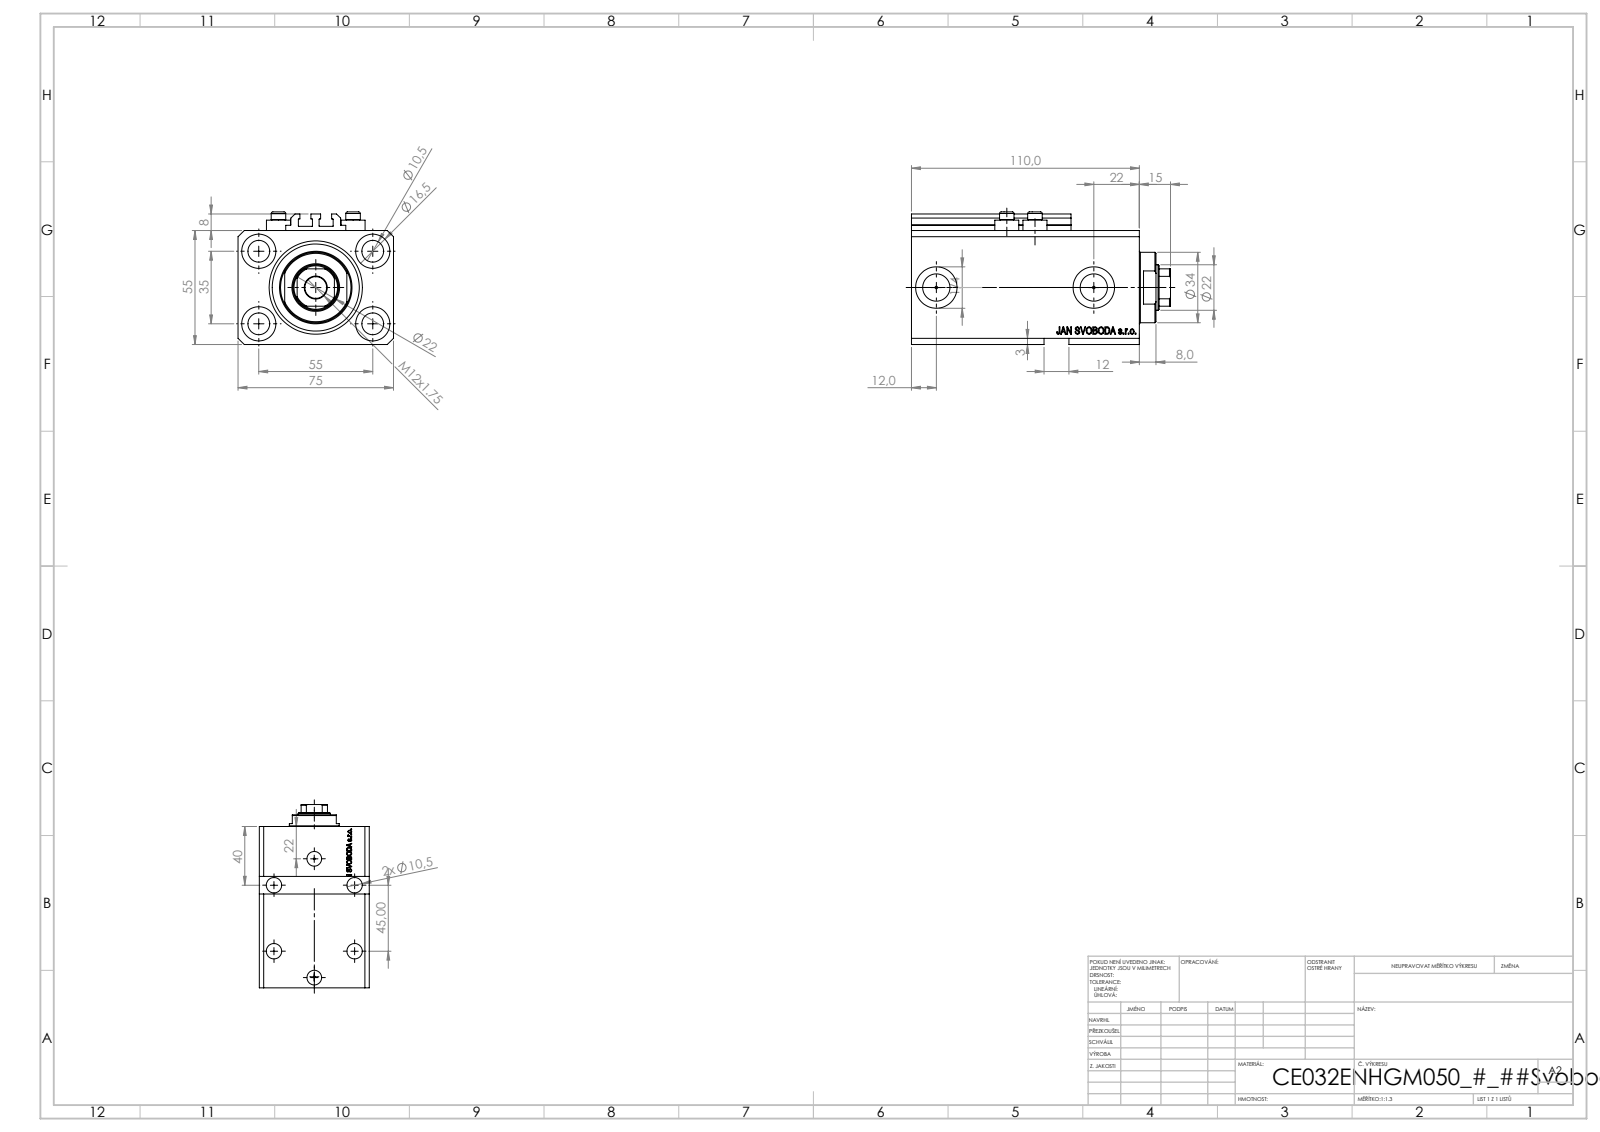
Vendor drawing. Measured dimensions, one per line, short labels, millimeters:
name: V250CE_E_Body; V250CE_C_VCP; V250CE_VC_E; ALLEN BOLT V250CE
written by: SolidWorks 2019 (CONFIG_CONTROL_DESIGN)
unit: mm
bodies: 8 solids, 1084 faces (514 planar, 146 cylindrical, 424 other)
size: 125 × 75 × 64
volume: 381 338 mm³; area: 95 642 mm²
holes: 9× ⌀10.5, 4× ⌀1.25, 4× ⌀4, 4× ⌀16.5, 2× ⌀10, 2× ⌀13.16, 2× ⌀20, 1× ⌀22, 1× ⌀32, 1× ⌀45
bosses: 4× ⌀11.6, 4× ⌀7, 1× ⌀34
rounds: 10× R0.2, 1× R10.5
face distances: 55, 75, 15, 110, 95, 3, 9.9, 85.1, 100.1, 57
hole spacings: 32.6, 32.87, 55, 68.74, 13.6, 14.09, 23.05, 25.81
